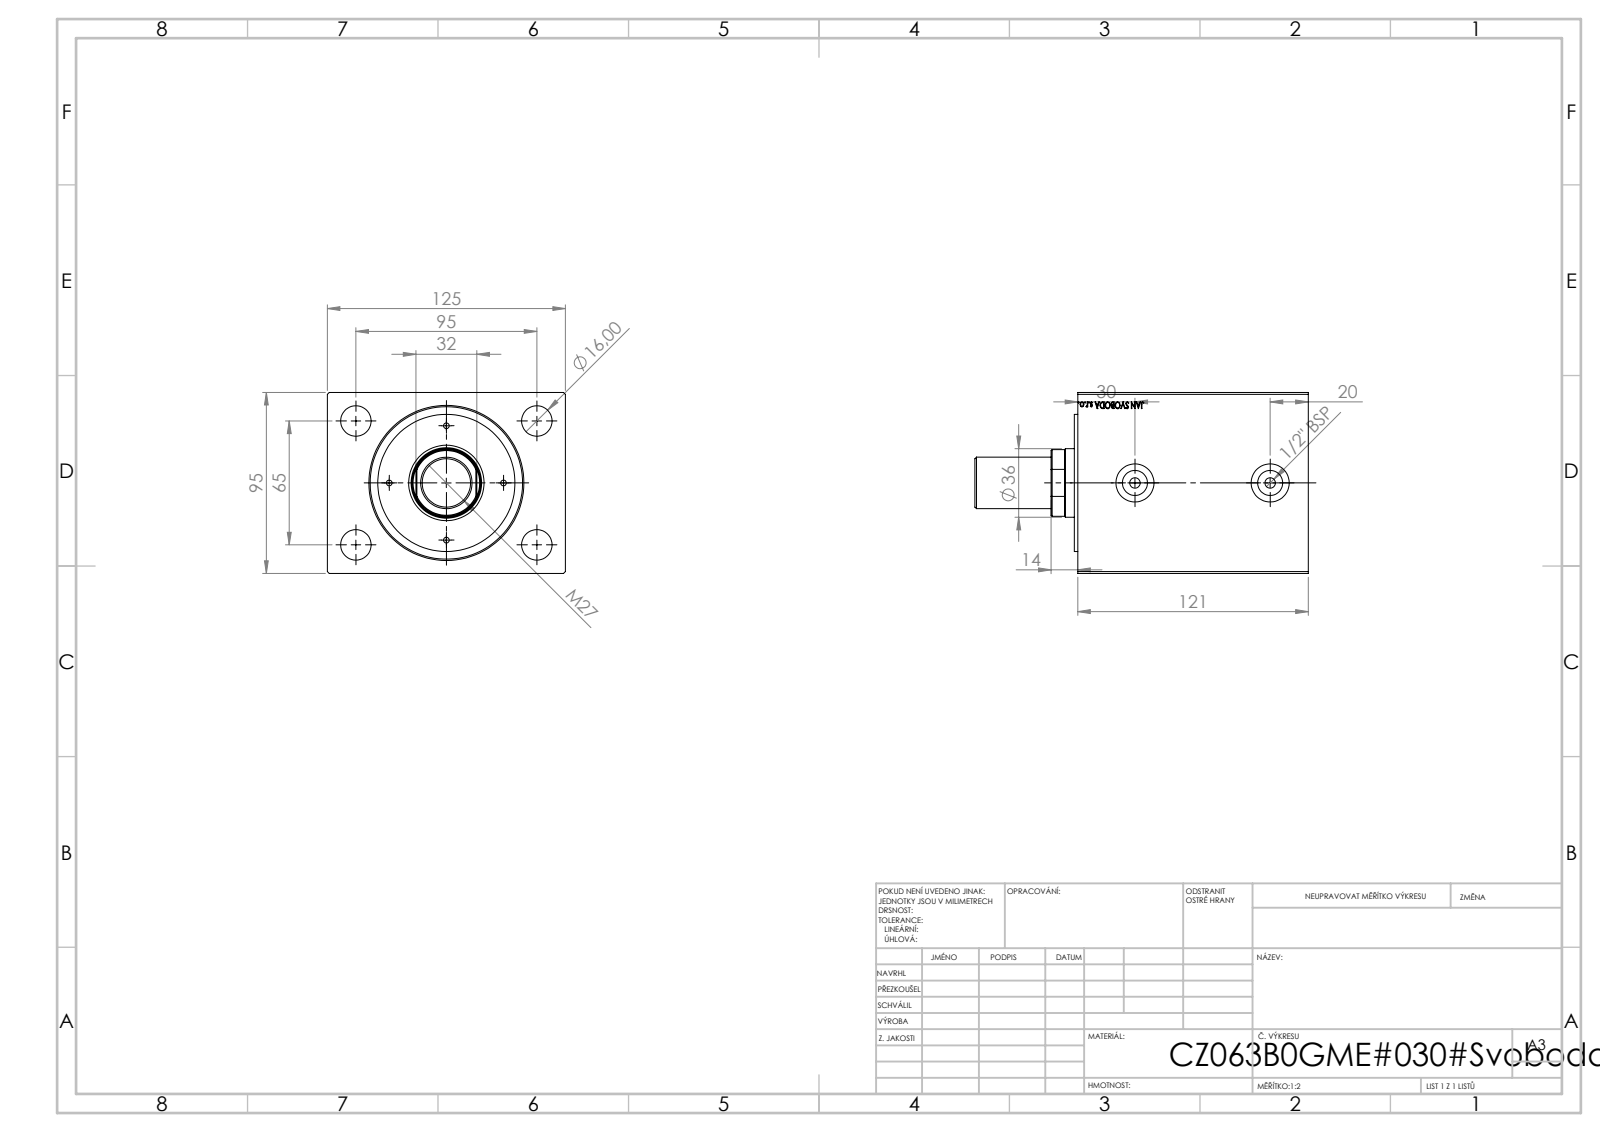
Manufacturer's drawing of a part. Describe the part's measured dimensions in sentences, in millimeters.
The part is named "V500CZ; V500CZ_SMALL_MALE_METRIC; V500CZ_B_VC". Its 3-D file was written by "SolidWorks 2019 (CONFIG_CONTROL_DESIGN)". It is 4 solids with 880 faces: 402 planar, 60 cylindrical and 418 other. Overall it measures 175 by 125 by 95 millimeters. Its volume is 1 338 000 cubic millimeters and its surface area 153 635 square millimeters. Round holes: 4 of diameter 3, 4 of diameter 16, 2 of diameter 5.5, 2 of diameter 13.16, 2 of diameter 20, 1 of diameter 25.5, 1 of diameter 36, 1 of diameter 37, 1 of diameter 63, 1 of diameter 80. Round bosses or shafts: 1 of diameter 72, 1 of diameter 27. Partial cylindrical surfaces (rounded edges, fillets, slot ends): 1 of radius 17.5. The main face-to-face distances are 95, 125, 121, 100.2, 20.8, 14, 12.2, 1.8, 88, 108.8. The hole center spacings are 30, 36.91, 42.43, 47.57, 57.55, 78.5, 84.04, 60.
